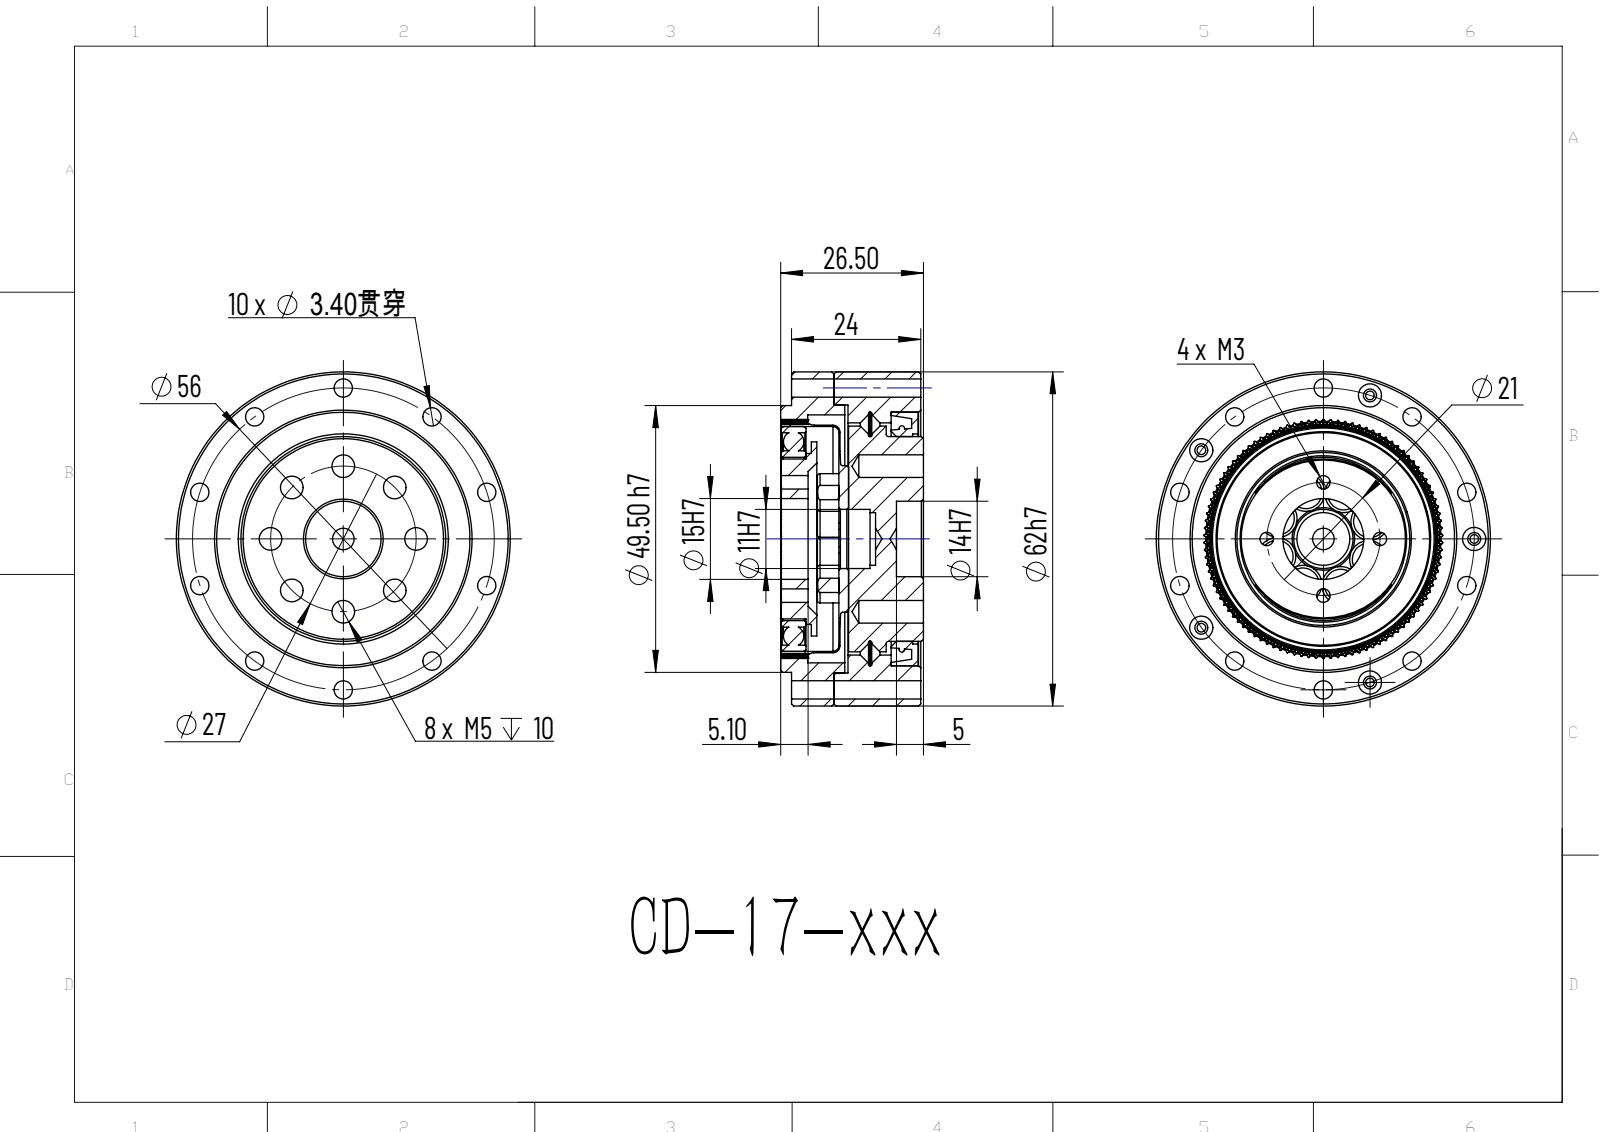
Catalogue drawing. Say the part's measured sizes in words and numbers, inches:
The part is named "CD-17; hexagon socket head cap screws gb_GB_FASTENER_SCREWS_HSHCS M4X8-N; CD-17-??; 17-???? <1> (+5 more)". Its 3-D file was written by "ONSHAPE BY PTC INC, 1.201 (AP242_MANAGED_MODEL_BASED_3D_ENGINEERING_MIM_LF)". It is 21 solids with 2397 faces: 625 planar, 1340 cylindrical and 432 other. Overall it measures 2.441 by 2.441 by 1.043 inches. Its volume is 3.434 cubic inches and its surface area 67.76 square inches. Round holes: 10 of diameter 0.134, 8 of diameter 0.13, 8 of diameter 0.165, 8 of diameter 0.177, 5 of diameter 0.063, 5 of diameter 0.094, 5 of diameter 0.169, 4 of diameter 0.098, 1 of diameter 0.081, 1 of diameter 0.114, 1 of diameter 0.197, 1 of diameter 0.386. Round bosses or shafts: 8 of diameter 0.276, 8 of diameter 0.157, 5 of diameter 0.15, 5 of diameter 0.079, 1 of diameter 2.441, 1 of diameter 1.949, 1 of diameter 1.662, 1 of diameter 1.65. Partial cylindrical surfaces (rounded edges, fillets, slot ends): 204 of radius 0.011, 204 of radius 0.072, 200 of radius 0.011, 200 of radius 0.012, 102 of radius 0.004, 1 of radius 0.835, 1 of radius 0.853, 1 of radius 0.857. The main face-to-face distances are 0.106, 0.035, 0.02, 0.311, 0.417, 0.071, 0.528, 0.598, 0.634, 0.346. The hole center spacings are 1.102, 2.097, 1.559, 2.178, 1.001, 1.965, 1.296, 0.158.
